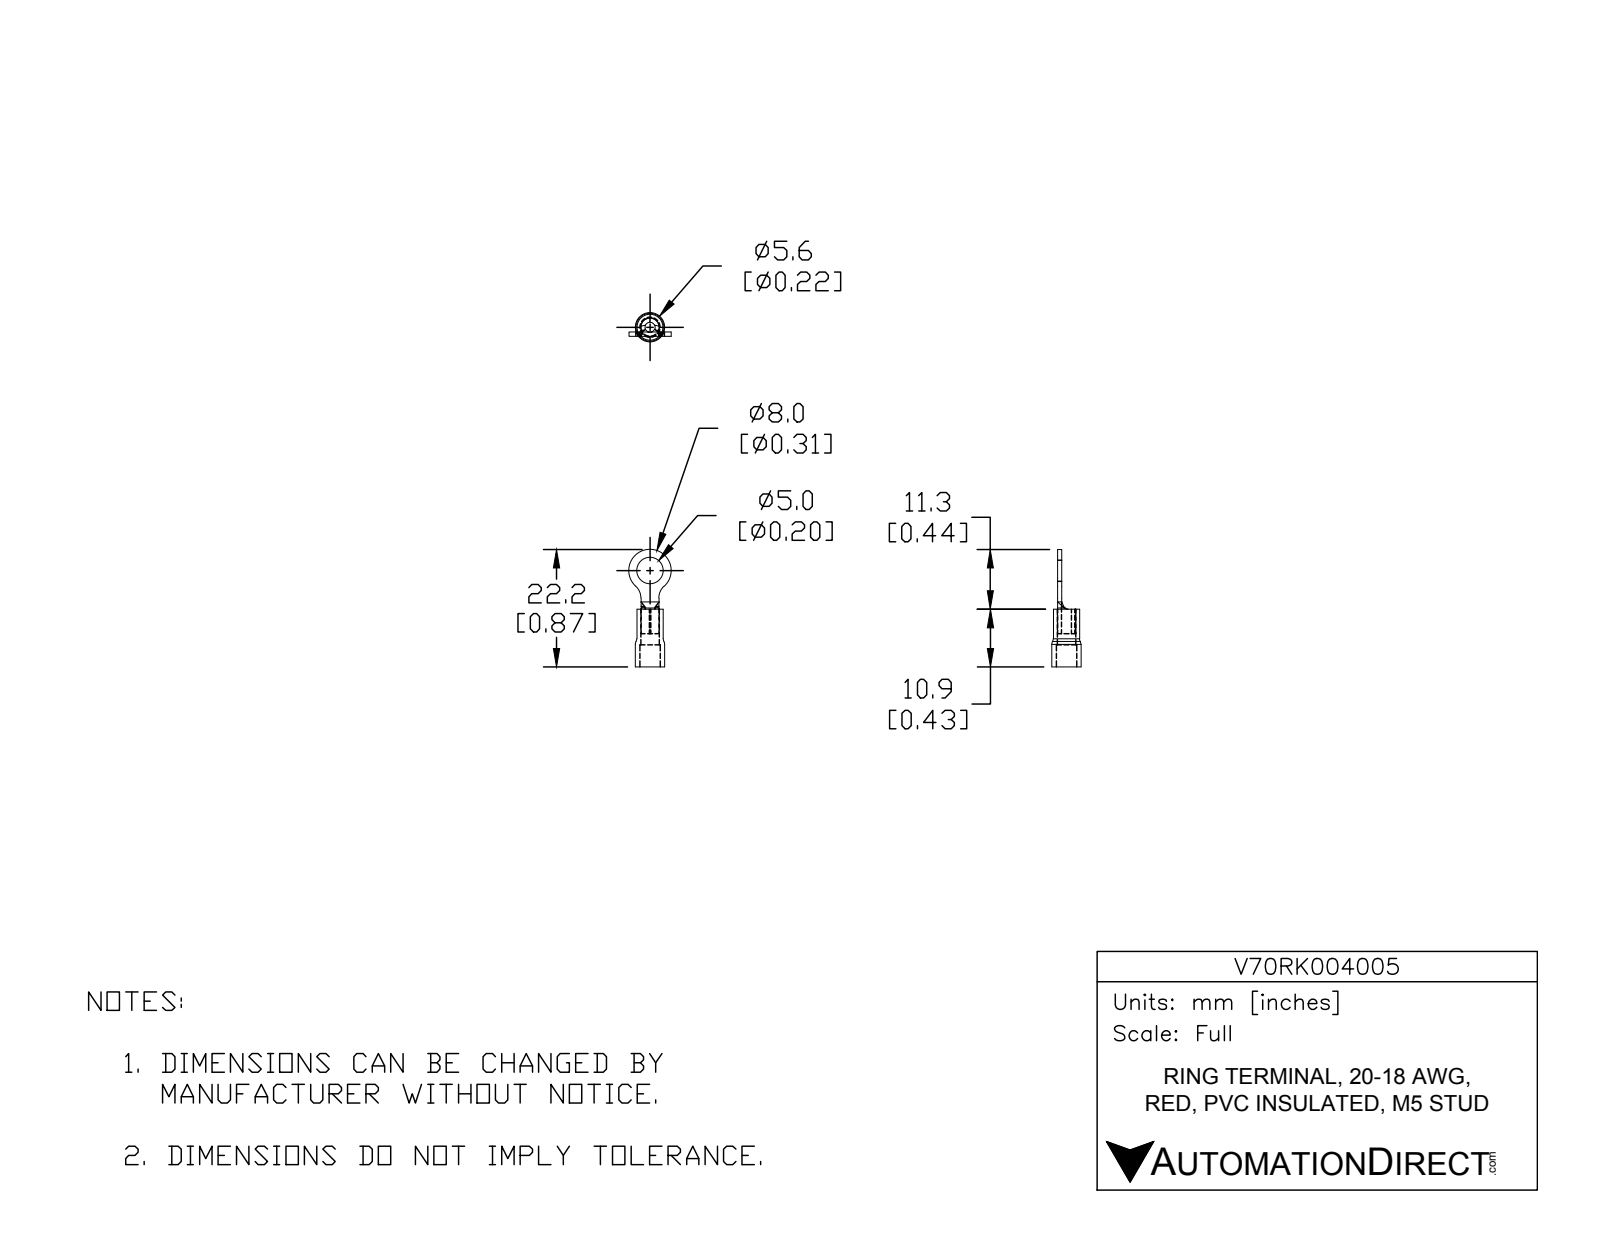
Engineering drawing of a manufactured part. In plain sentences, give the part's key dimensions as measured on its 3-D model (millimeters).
The part is named "V70RK004005". Its 3-D file was written by "SolidWorks 2017 (AUTOMOTIVE_DESIGN)". It is 2 solids with 45 faces: 12 planar, 21 cylindrical and 12 other. Overall it measures 22.2 by 8 by 5.55 millimeters. Its volume is 183 cubic millimeters and its surface area 542 square millimeters. Round holes: 1 of diameter 1.9, 1 of diameter 3.5, 1 of diameter 3.85, 1 of diameter 5. Round bosses or shafts: 1 of diameter 5.55, 1 of diameter 4.95, 1 of diameter 3.4. Partial cylindrical surfaces (rounded edges, fillets, slot ends): 2 of radius 0.1, 2 of radius 3, 1 of radius 4. The main face-to-face distances are 0.8, 10.9, 6.3, 4.6, 4.15, 2.15, 6.75, 1.73, 1.68, 1.69.
